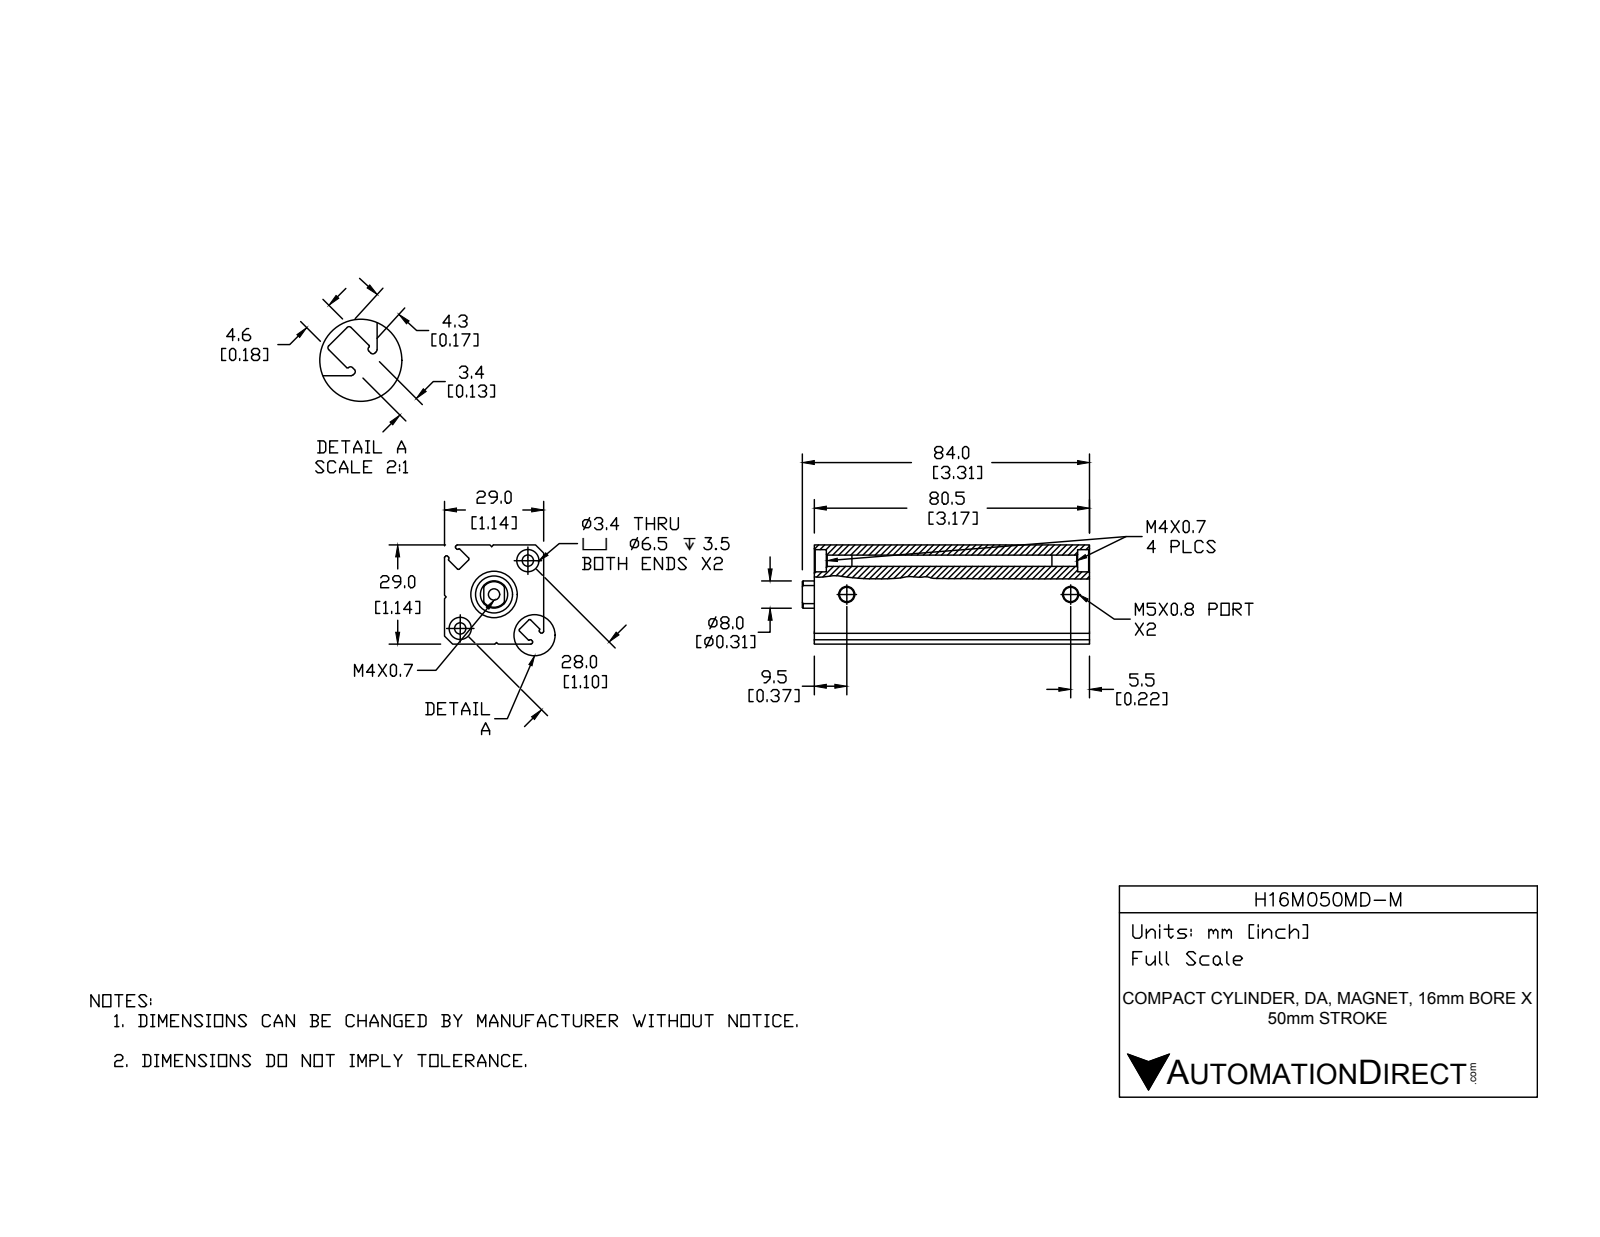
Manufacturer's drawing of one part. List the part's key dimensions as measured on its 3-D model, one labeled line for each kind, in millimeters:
Part name (STEP PRODUCT): H16M050MD-M; H16M050MD-M-PISTON; H16M050MD-M-BODY
STEP written by: SolidWorks 2015 (CONFIG_CONTROL_DESIGN)
Units: millimetres
Bodies: 2 solids, 128 faces (49 planar, 54 cylindrical, 25 other)
Overall size (bounding box): 84 × 29 × 29
Volume: 52 587 mm³ · Surface area: 21 250 mm²
Round holes (diameter × count): ⌀3.3 ×3, ⌀4.2 ×2, ⌀6.5 ×2, ⌀8 ×1, ⌀13.6 ×1, ⌀16 ×1
Round bosses / shafts (diameter × count): ⌀10.8 ×1
Partial cylindrical surfaces — rounded edges, fillets, slot ends (radius × count): R0.4 ×16, R0.2 ×4
Main face-to-face distances: 29, 4.6, 80.5, 4, 16.53, 21.13, 76.5, 24.84, 37.66, 20.2
Hole centre spacings: 14, 28, 65.5
